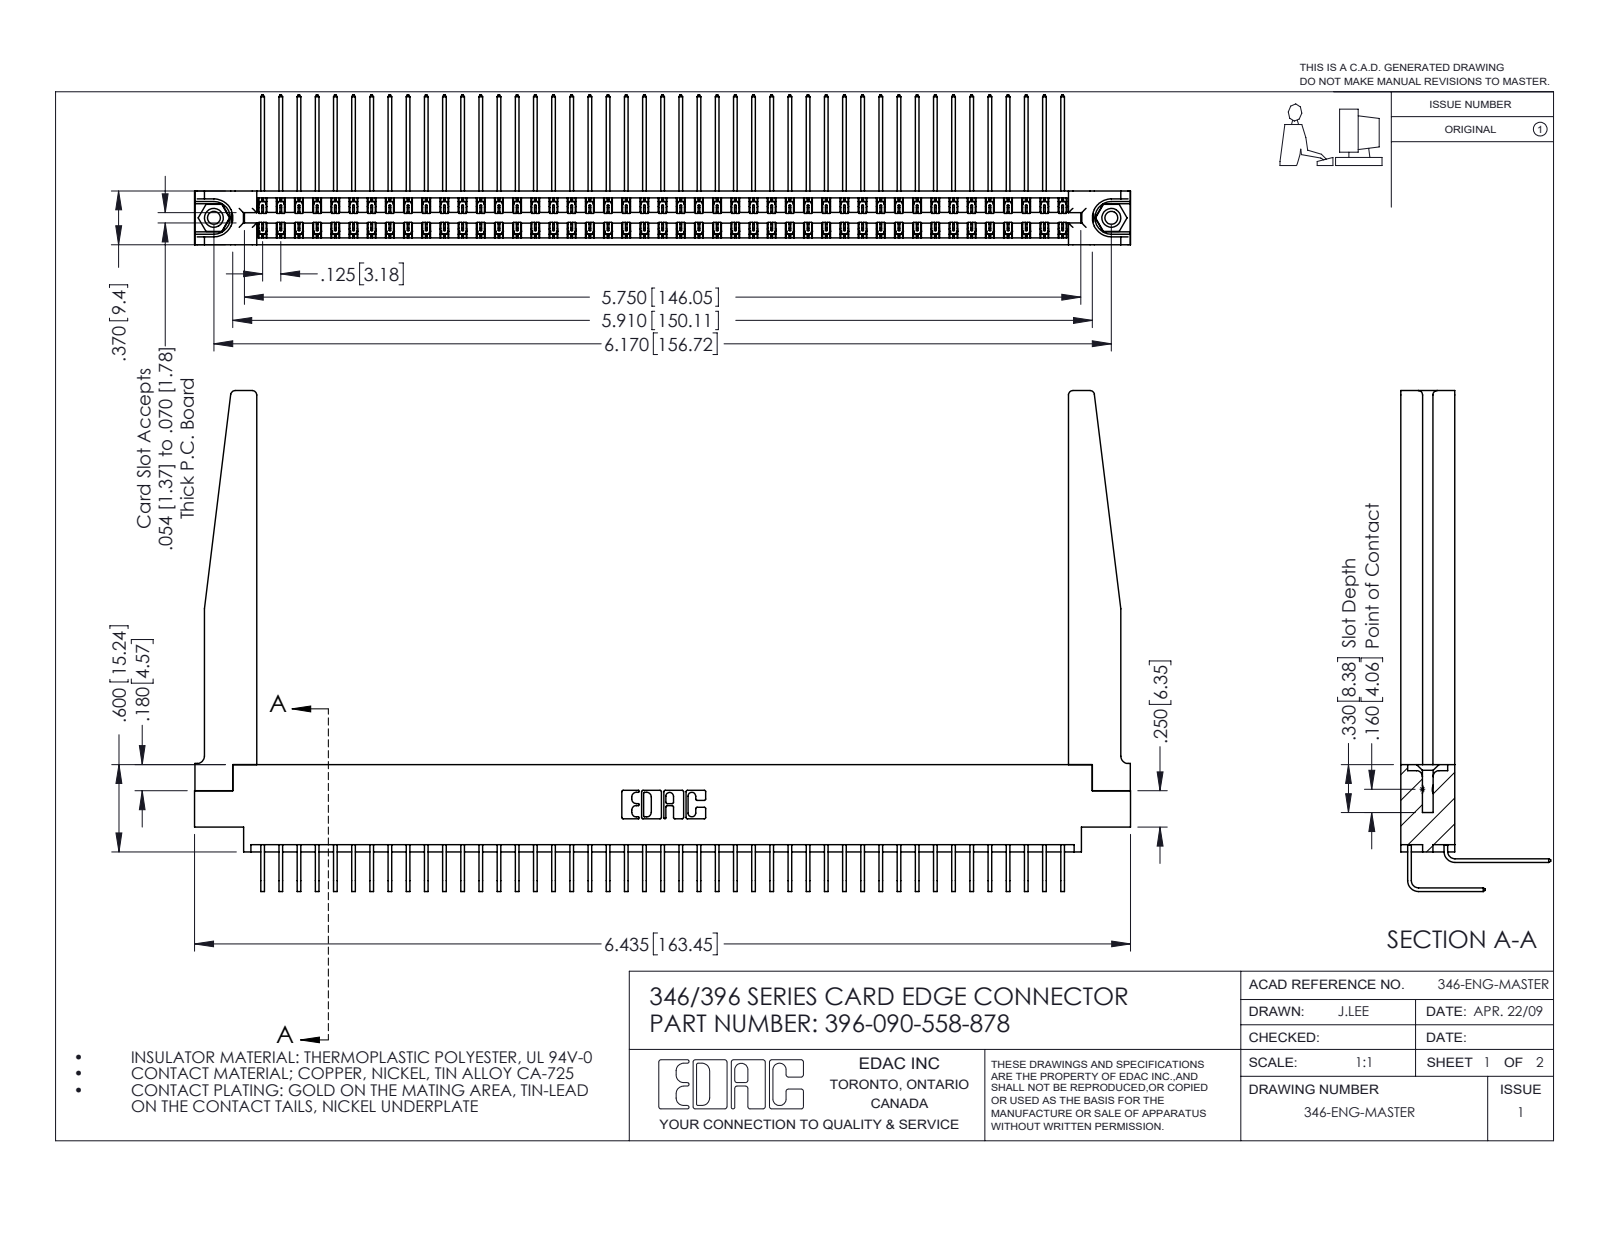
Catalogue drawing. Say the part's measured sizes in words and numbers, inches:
The part is named "345-292-001_558 559 Tail - 1; 345-292-001_558 Tail - 2; 346-220-078_345-220-078; 346 Part_0.170 Offset - 0.156 Dia-TH (+2 more)". Its 3-D file was written by "SolidWorks 2016 (CONFIG_CONTROL_DESIGN)". It is 95 solids with 5220 faces: 3552 planar, 1616 cylindrical and 52 other. Overall it measures 6.435 by 3.443 by 1.03 inches. Its volume is 1.418 cubic inches and its surface area 49.13 square inches. Round holes: 2 of diameter 0.089, 2 of diameter 0.125, 2 of diameter 0.156, 1 of diameter 0.064. Round bosses or shafts: 2 of diameter 0.155. Partial cylindrical surfaces (rounded edges, fillets, slot ends): 135 of radius 0.006, 22 of radius 0.01, 8 of radius 0.03, 6 of radius 0.007, 6 of radius 0.031, 4 of radius 0.05, 3 of radius 0.026, 2 of radius 0.014. The main face-to-face distances are 0.37, 0.322, 0.048, 0.072, 0.025, 0.298, 0.25, 0.148, 0.15, 0.275. The hole center spacings are 0.246, 5.961, 6.17.
